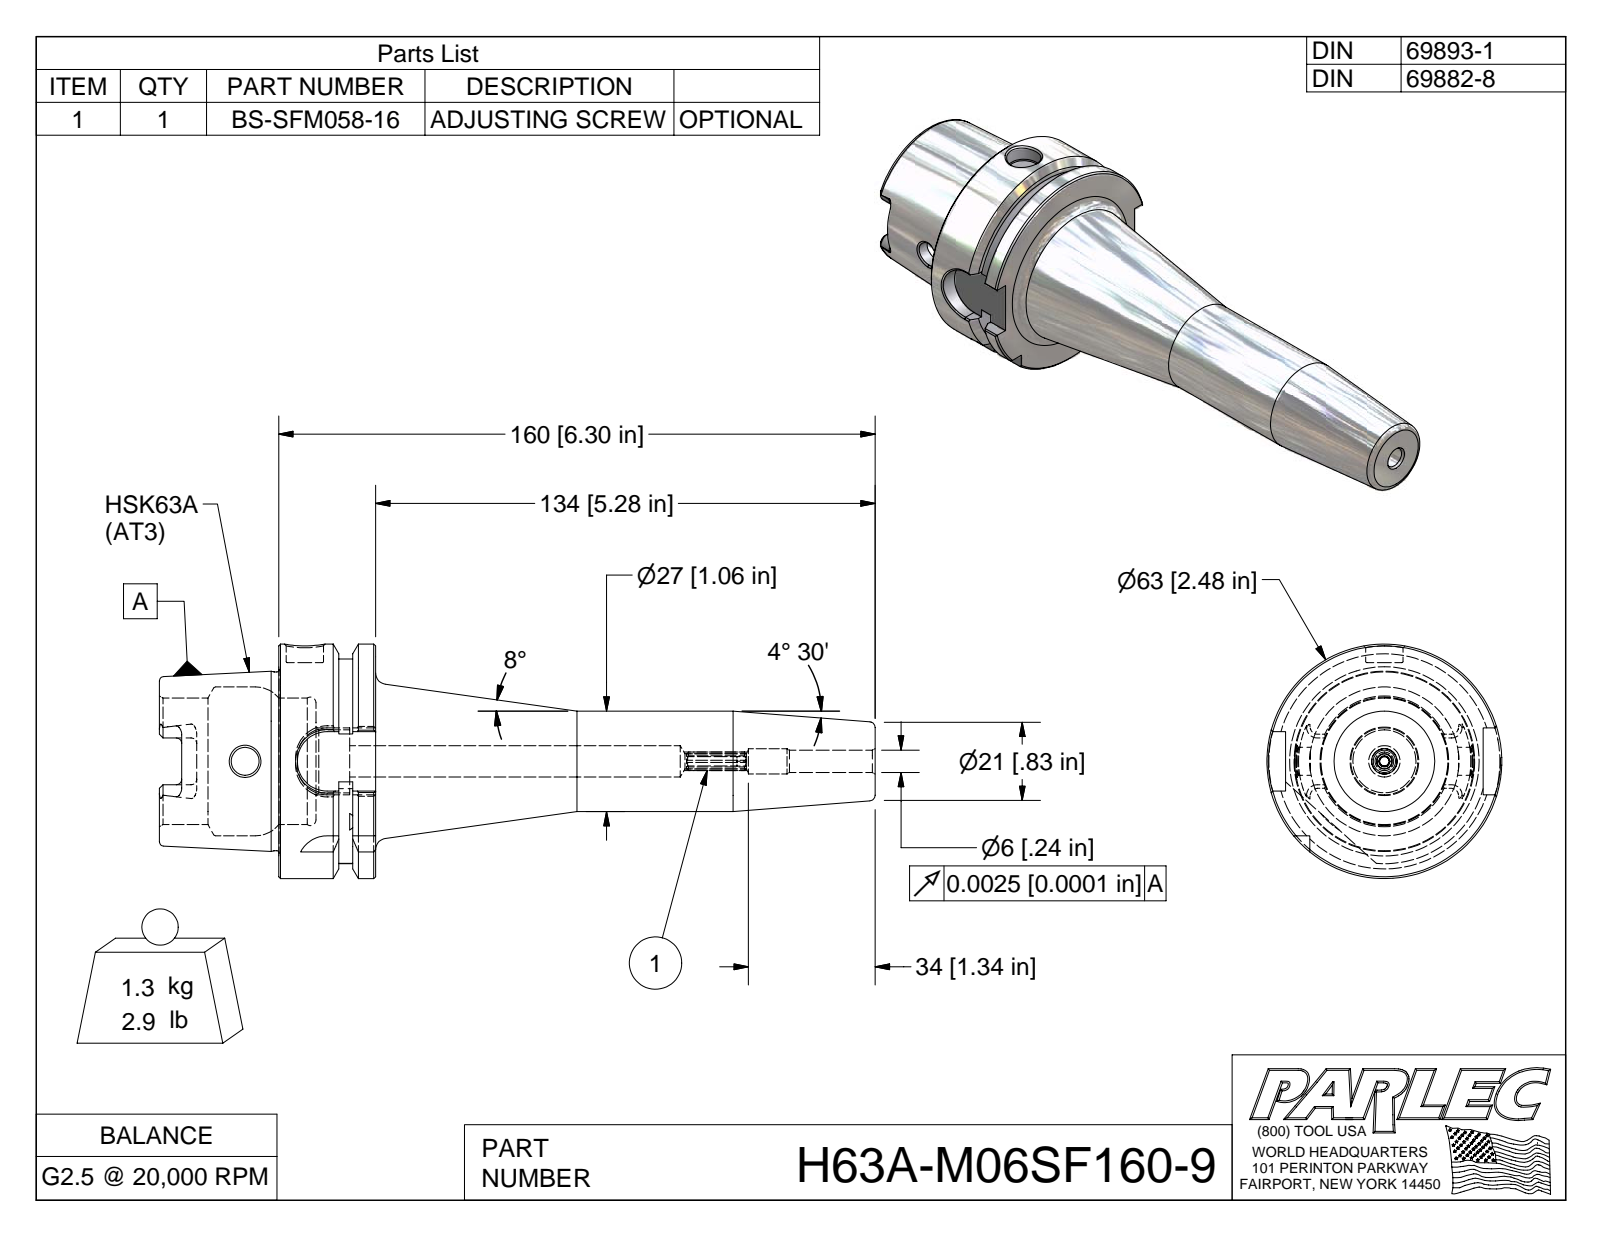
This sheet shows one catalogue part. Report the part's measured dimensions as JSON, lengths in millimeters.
{"part_name": "H63A-M06SF160-9; H63A-M06SF160-9-1; BS-SFM058-16", "step_written_by": "Autodesk Inventor 2009 (AUTOMOTIVE_DESIGN)", "units": "millimeters", "bodies": {"solids": 2, "faces": 160, "planar": 59, "cylindrical": 35, "other": 66}, "overall_size": [192, 63, 63], "volume_mm3": 169100, "surface_area_mm2": 36970, "round_holes": [[6, 1], [6.8, 1], [7.5, 1], [10, 1], [16.9, 1], [34, 1], [40, 1]], "round_bosses_or_shafts": [[63, 1], [48, 1], [27, 1]], "partial_cylinders_radius": [[1.5, 6], [2.9, 4], [8, 4], [2.5, 1], [27.5, 1]], "face_to_face_distances": [26, 6.1, 9.9, 10, 16, 32, 42, 58, 48.1, 16.1]}
